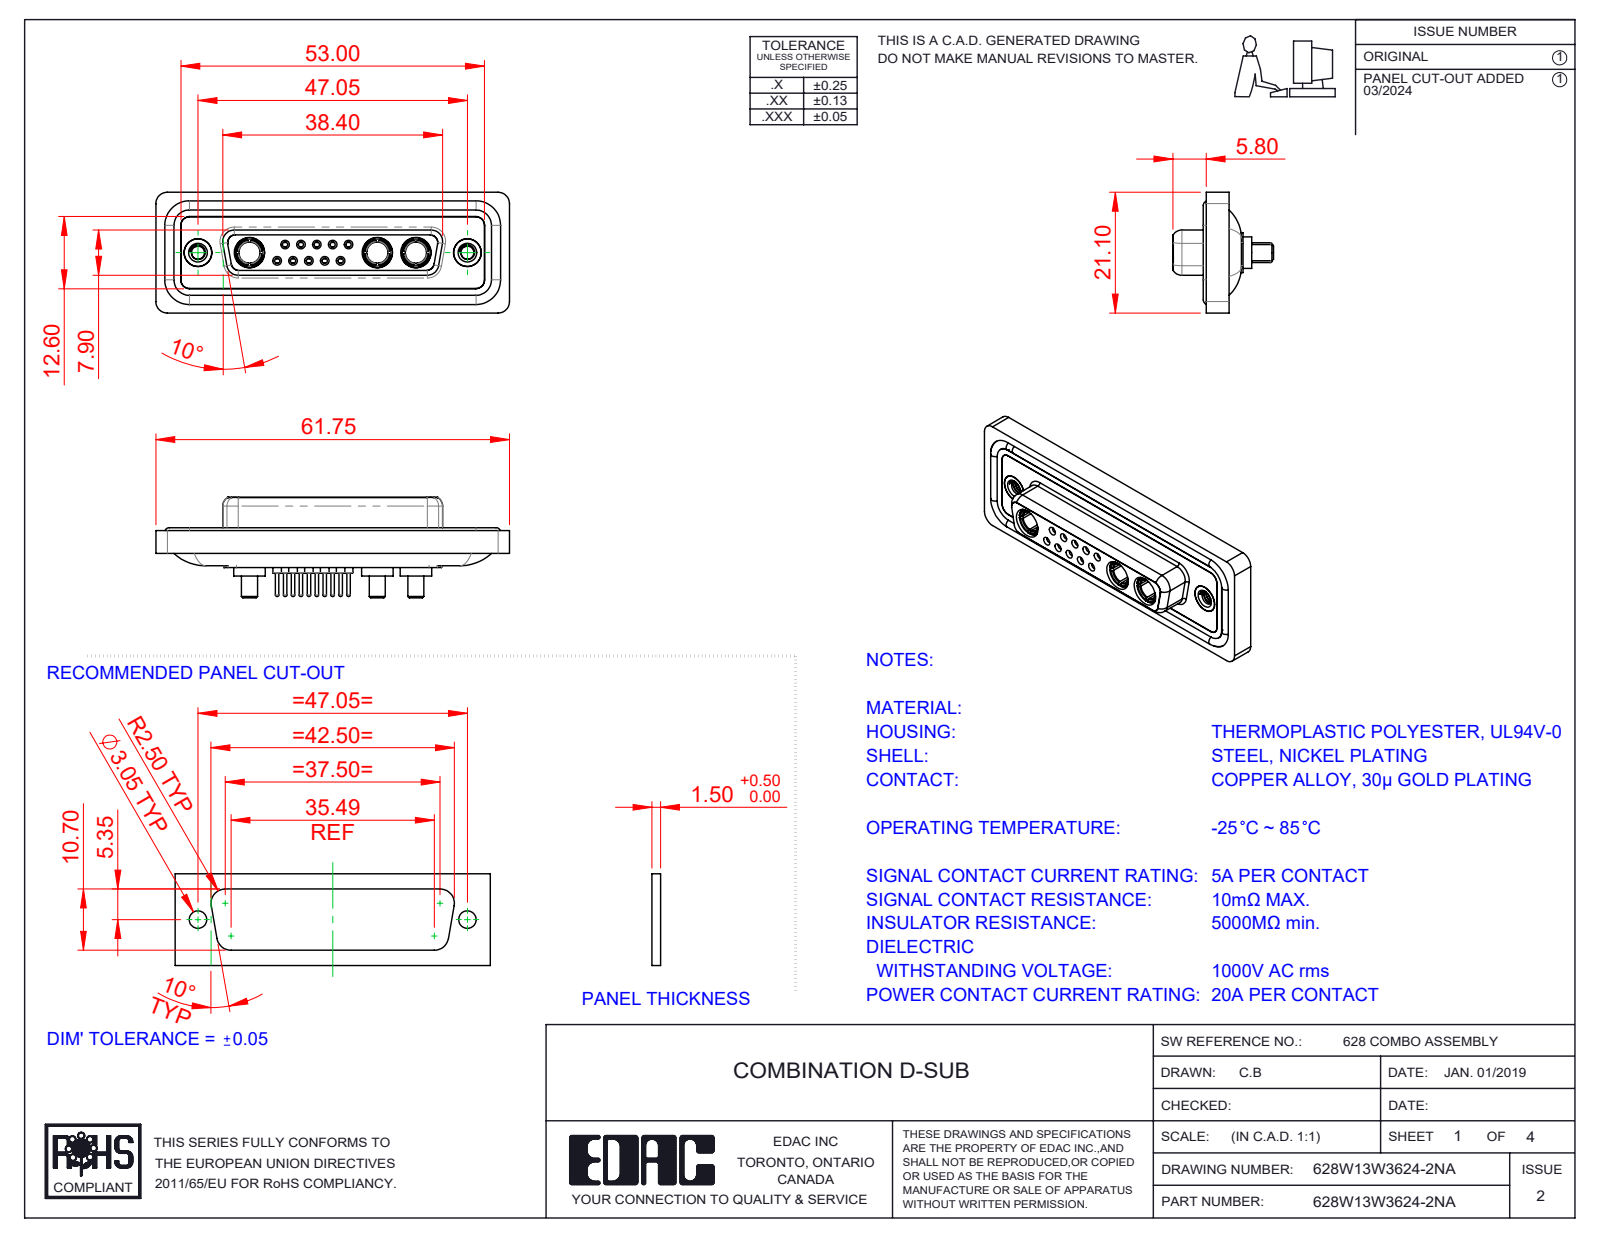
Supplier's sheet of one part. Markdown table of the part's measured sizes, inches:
| quantity | value |
| --- | --- |
| part name | 628Combo Contact Row 1_24; 628W13W3624-2NA; Power Socket_20A S; 628Combo Threaded Rivet_A (+5 more) |
| STEP written by | SolidWorks 2023 (CONFIG_CONTROL_DESIGN) |
| units | inches |
| bodies | 23 solids, 1156 faces (342 planar, 449 cylindrical, 365 other) |
| overall size | 2.431 × 0.831 × 0.691 |
| volume | 0.505 in³ |
| surface area | 21.24 in² |
| round holes (diameter × count) | 0.035 × 10, 0.043 × 10, 0.059 × 10, 0.079 × 10, 0.063 × 5, 0.067 × 5, 0.191 × 5, 0.146 × 3, 0.209 × 3, 0.089 × 2, 0.157 × 2, 0.159 × 2 |
| round bosses / shafts (diameter × count) | 0.087 × 10, 0.024 × 10, 0.063 × 9, 0.217 × 3, 0.205 × 3, 0.195 × 3, 0.187 × 3, 0.148 × 3 |
| partial cylindrical surfaces (radius × count) | 0.059 × 22, 0.079 × 18, 0.053 × 8, 0.063 × 8, 0.01 × 4, 0.02 × 4, 0.024 × 4, 0.026 × 4 |
| main face-to-face distances | 0.016, 0.071, 0.293, 0.222, 0.02, 0.26, 0.278, 0.063, 0.114, 0.043 |
| hole center spacings | 0.124, 0.109, 0.198, 0.198, 0.218, 0.327, 0.295, 0.109 |
